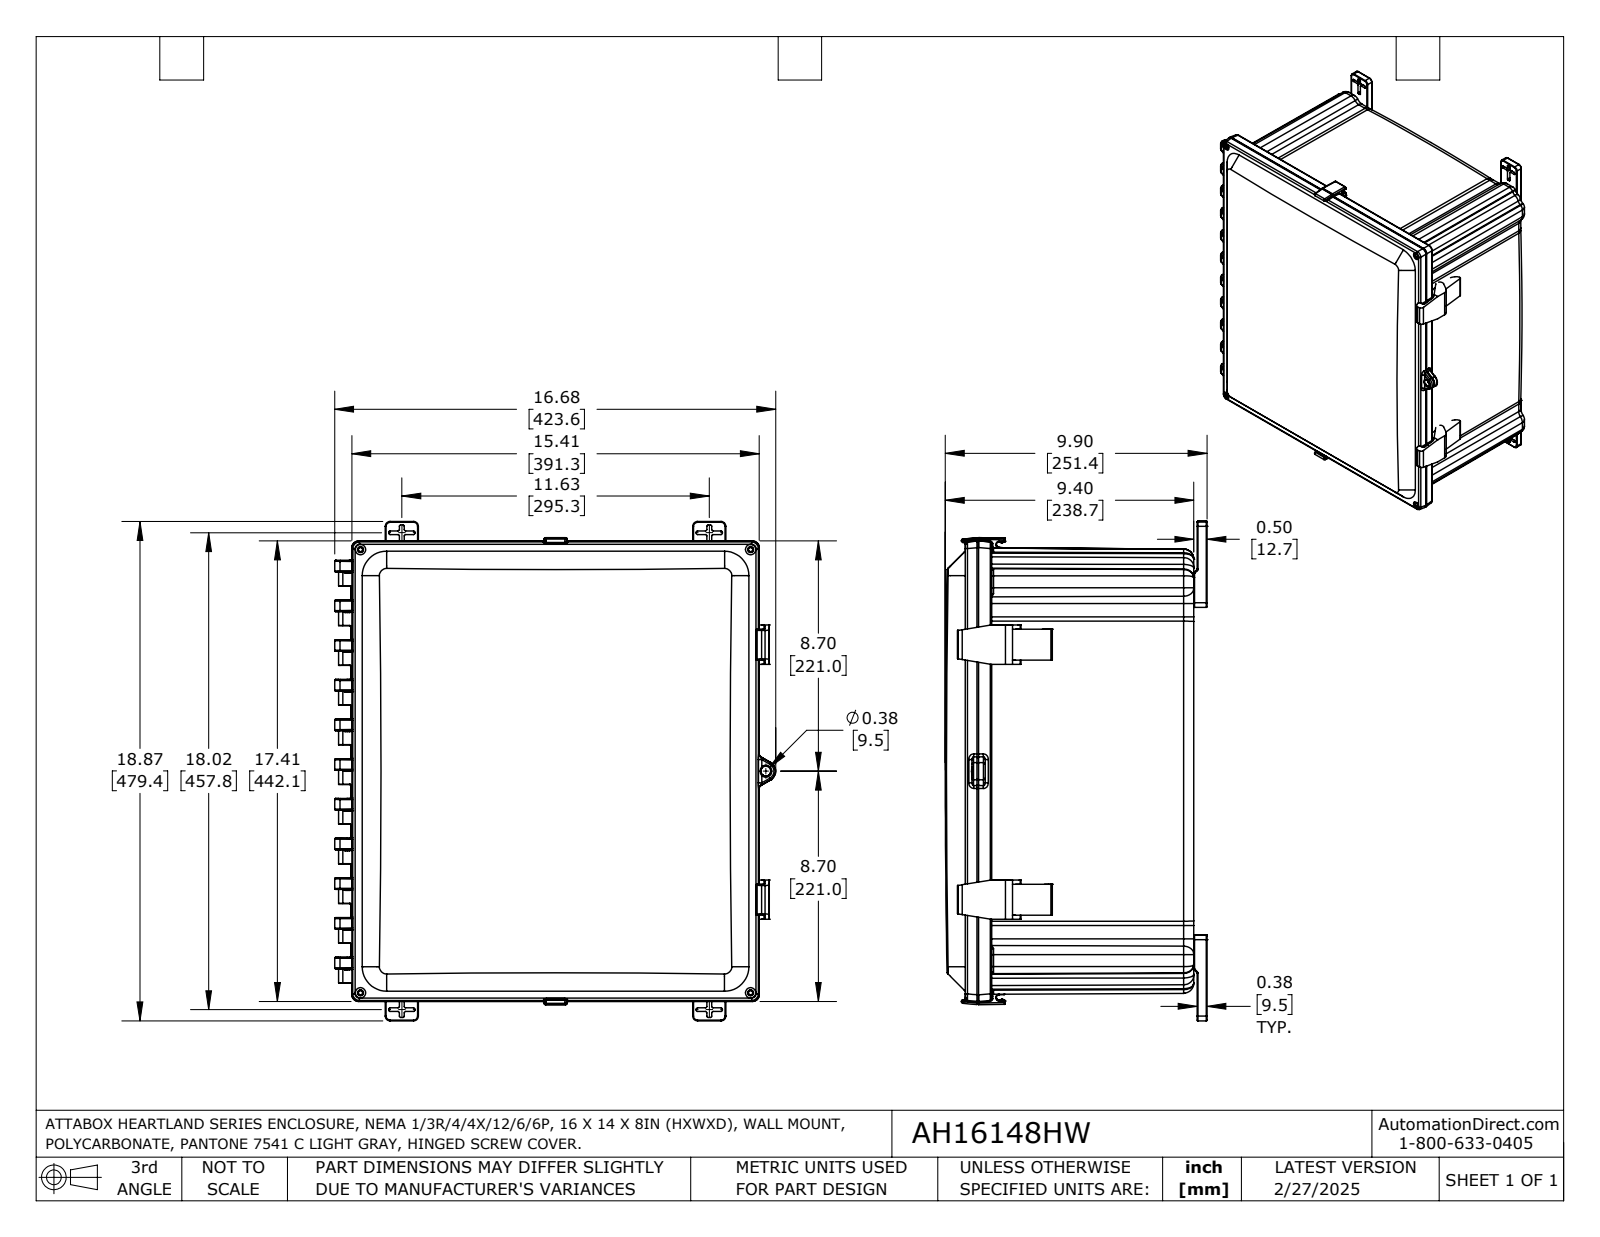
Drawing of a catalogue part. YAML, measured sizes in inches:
part_name: "AH16148HW"
step_written_by: "SolidWorks 2024 (AUTOMOTIVE_DESIGN)"
units: inches
bodies: {solids: 6, faces: 3102, planar: 818, cylindrical: 1010, other: 1274}
overall_size: [18.875, 16.676, 9.898]
volume: 200.3
surface_area: 2325
round_holes:
  - {diameter: 0.156, count: 8}
  - {diameter: 0.25, count: 4}
  - {diameter: 0.313, count: 4}
  - {diameter: 0.39, count: 4}
  - {diameter: 0.195, count: 3}
  - {diameter: 0.375, count: 2}
  - {diameter: 0.195, count: 1}
  - {diameter: 0.327, count: 1}
  - {diameter: 0.45, count: 1}
round_bosses_or_shafts:
  - {diameter: 0.25, count: 4}
  - {diameter: 0.313, count: 1}
partial_cylinders:
  - {radius: 0.035, count: 166}
  - {radius: 0.065, count: 125}
  - {radius: 0.05, count: 118}
  - {radius: 0.02, count: 85}
  - {radius: 0.03, count: 84}
  - {radius: 0.025, count: 48}
  - {radius: 0.008, count: 24}
  - {radius: 0.01, count: 23}
face_to_face_distances: [0.14, 8.14, 8, 0.5, 0.187, 8.64, 0.43, 7.5, 7.64, 0.29]
hole_center_spacings: [13.28, 13.558, 17.464, 20.555, 0.442, 1.768, 2.21, 11.941]
